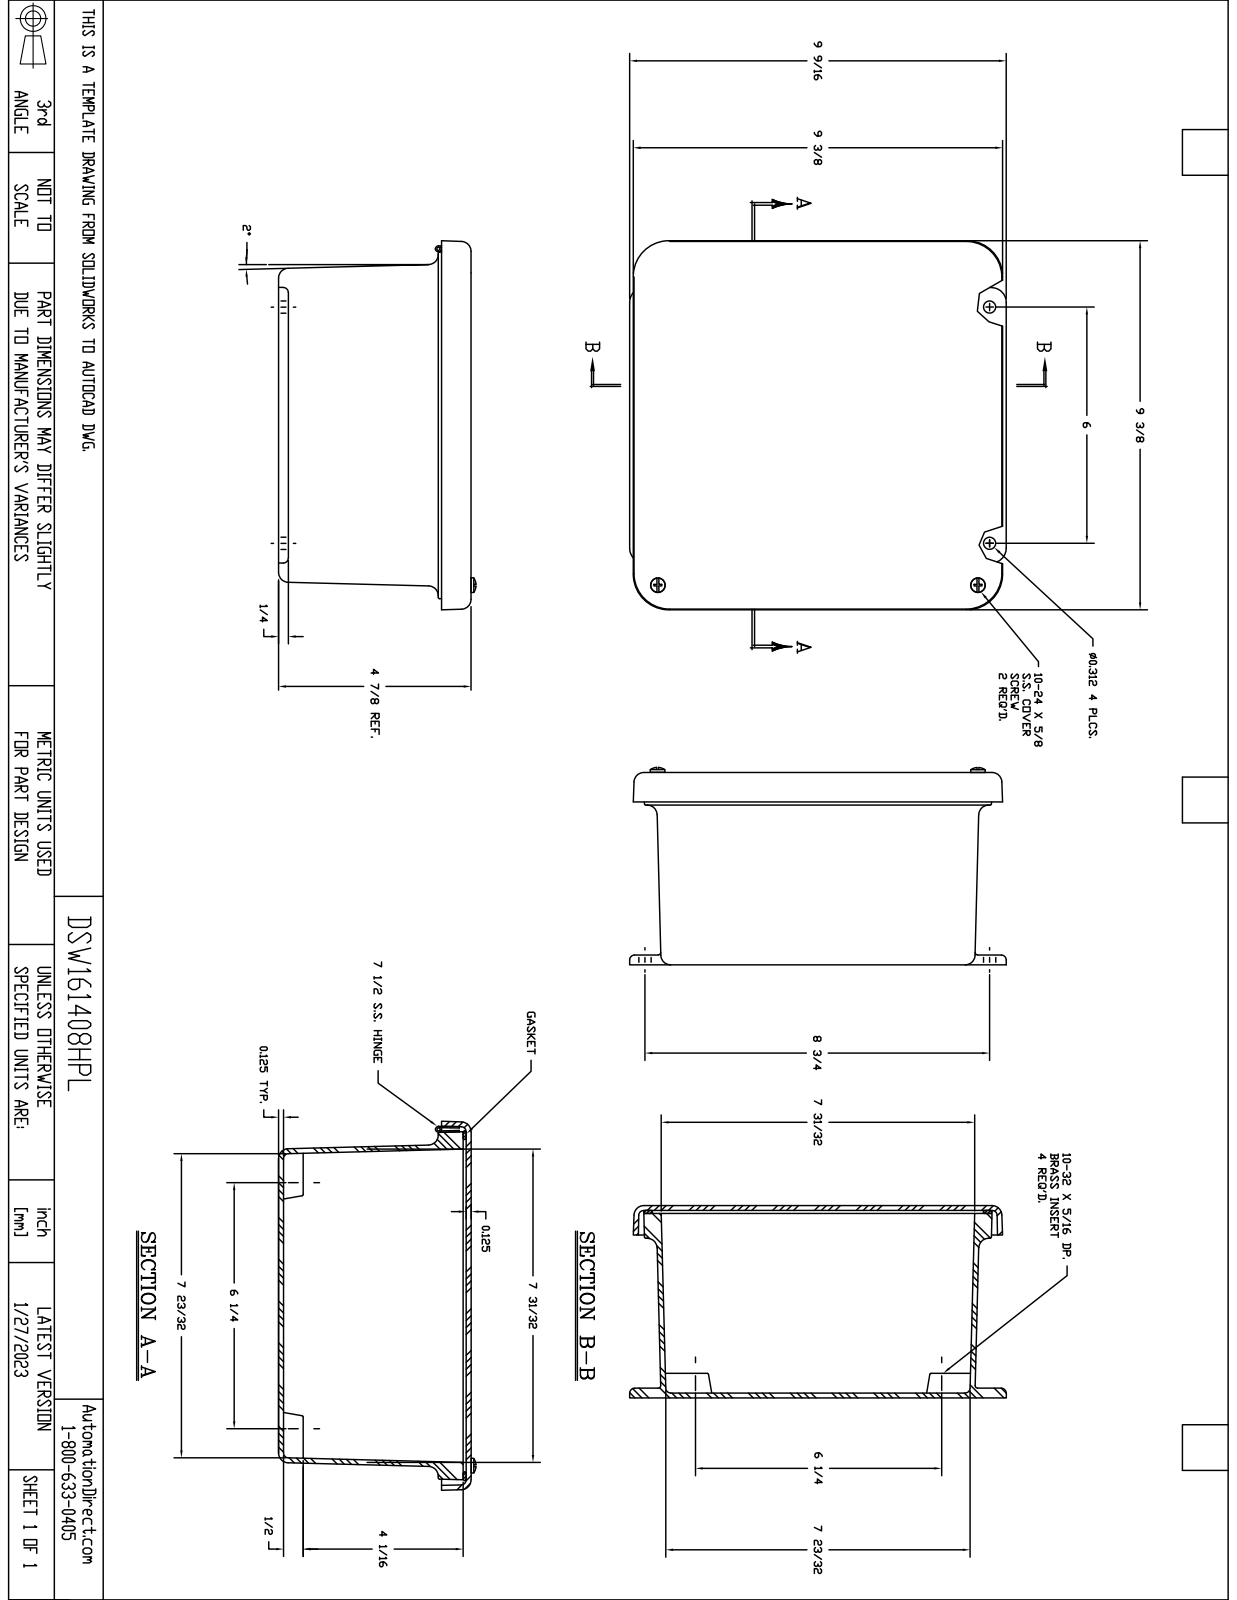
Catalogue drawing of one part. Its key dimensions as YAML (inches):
part_name: "M808HW"
step_written_by: "SolidWorks 2018 (AUTOMOTIVE_DESIGN)"
units: inches
bodies: {solids: 20, faces: 797, planar: 244, cylindrical: 302, other: 251}
overall_size: [9.562, 9.407, 5.018]
volume: 51.48
surface_area: 736.6
round_holes:
  - {diameter: 0.152, count: 8}
  - {diameter: 0.131, count: 6}
  - {diameter: 0.14, count: 6}
  - {diameter: 0.156, count: 4}
  - {diameter: 0.218, count: 4}
  - {diameter: 0.145, count: 2}
  - {diameter: 0.085, count: 1}
  - {diameter: 0.085, count: 1}
round_bosses_or_shafts:
  - {diameter: 0.27, count: 6}
  - {diameter: 0.25, count: 6}
  - {diameter: 0.125, count: 4}
  - {diameter: 0.19, count: 2}
  - {diameter: 0.156, count: 2}
  - {diameter: 0.125, count: 2}
  - {diameter: 0.155, count: 1}
partial_cylinders:
  - {radius: 0.031, count: 36}
  - {radius: 0.125, count: 12}
  - {radius: 0.25, count: 12}
  - {radius: 0.2, count: 6}
  - {radius: 0.031, count: 4}
  - {radius: 0.375, count: 4}
  - {radius: 0.063, count: 2}
face_to_face_distances: [0.125, 4.763, 4.887, 4.637, 0.125, 4.762, 4.56, 0.202, 0.078, 4.685]
hole_center_spacings: [7.249, 3.5, 1.326, 6.25, 8.125, 10.165, 0.25, 3.25]
